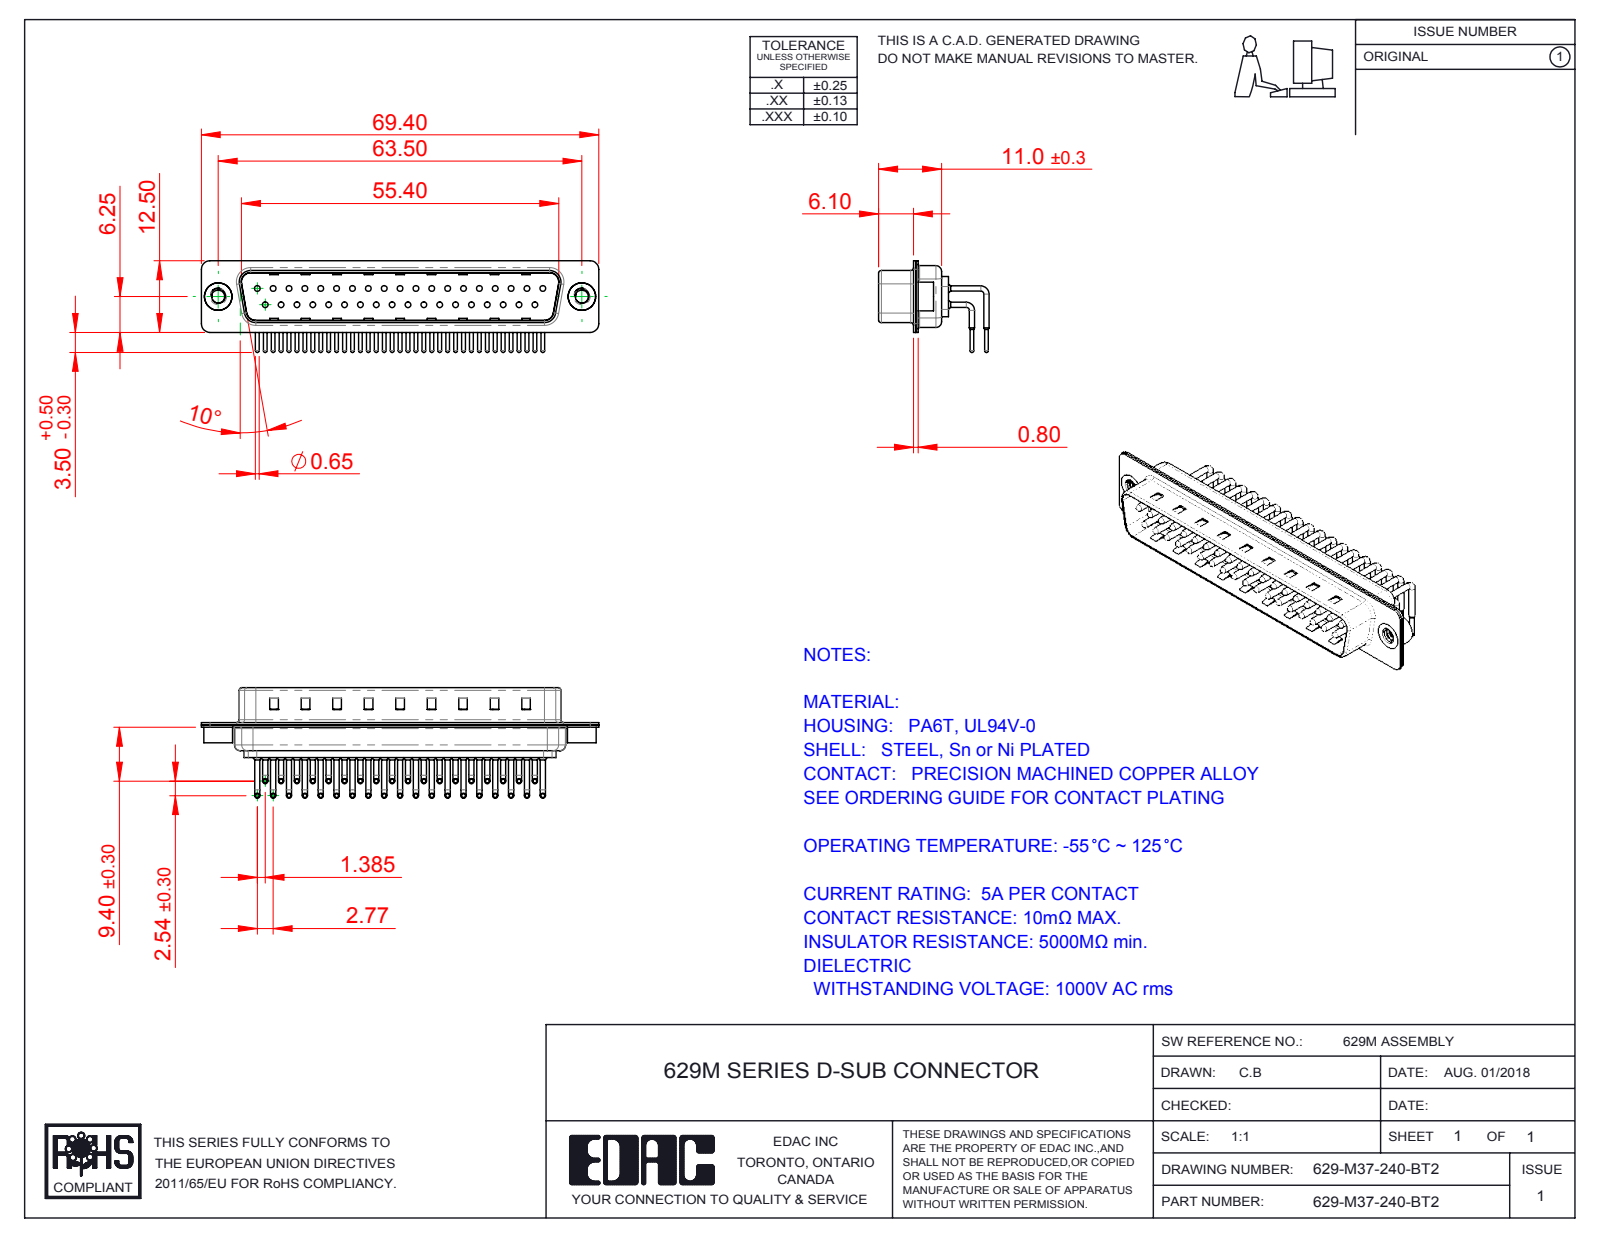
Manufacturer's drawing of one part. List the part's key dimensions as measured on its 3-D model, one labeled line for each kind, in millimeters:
Part name (STEP PRODUCT): 629M Shell Rear_37 Contacts; 629M Contact Row 1; 629M Contact Row 2; 629M Shell Front_37 Contacts (+3 more)
STEP written by: SolidWorks 2016 (CONFIG_CONTROL_DESIGN)
Units: millimetres
Bodies: 42 solids, 4482 faces (2571 planar, 1473 cylindrical, 438 other)
Overall size (bounding box): 69.4 × 19.29 × 16
Volume: 4 051 mm³ · Surface area: 10 620 mm²
Round holes (diameter × count): ⌀1 ×37, ⌀1.7 ×37, ⌀2 ×37, ⌀2.26 ×2, ⌀4 ×2, ⌀4.8 ×2
Round bosses / shafts (diameter × count): ⌀0.9 ×74, ⌀1.5 ×37, ⌀0.65 ×37, ⌀5 ×2, ⌀4.9 ×2
Partial cylindrical surfaces — rounded edges, fillets, slot ends (radius × count): R1.01 ×37, R1.5 ×16, R2 ×12, R0.5 ×8, R1.6 ×8, R0.25 ×4, R0.6 ×4, R0.65 ×4
Main face-to-face distances: 0.4, 0.85, 9.55, 8.7, 1.25, 10.4, 1.5, 1.9, 0.35, 9.95
Hole centre spacings: 3.16, 2.77, 5.54, 8.31, 5.04, 10.1, 11.08, 12.78
